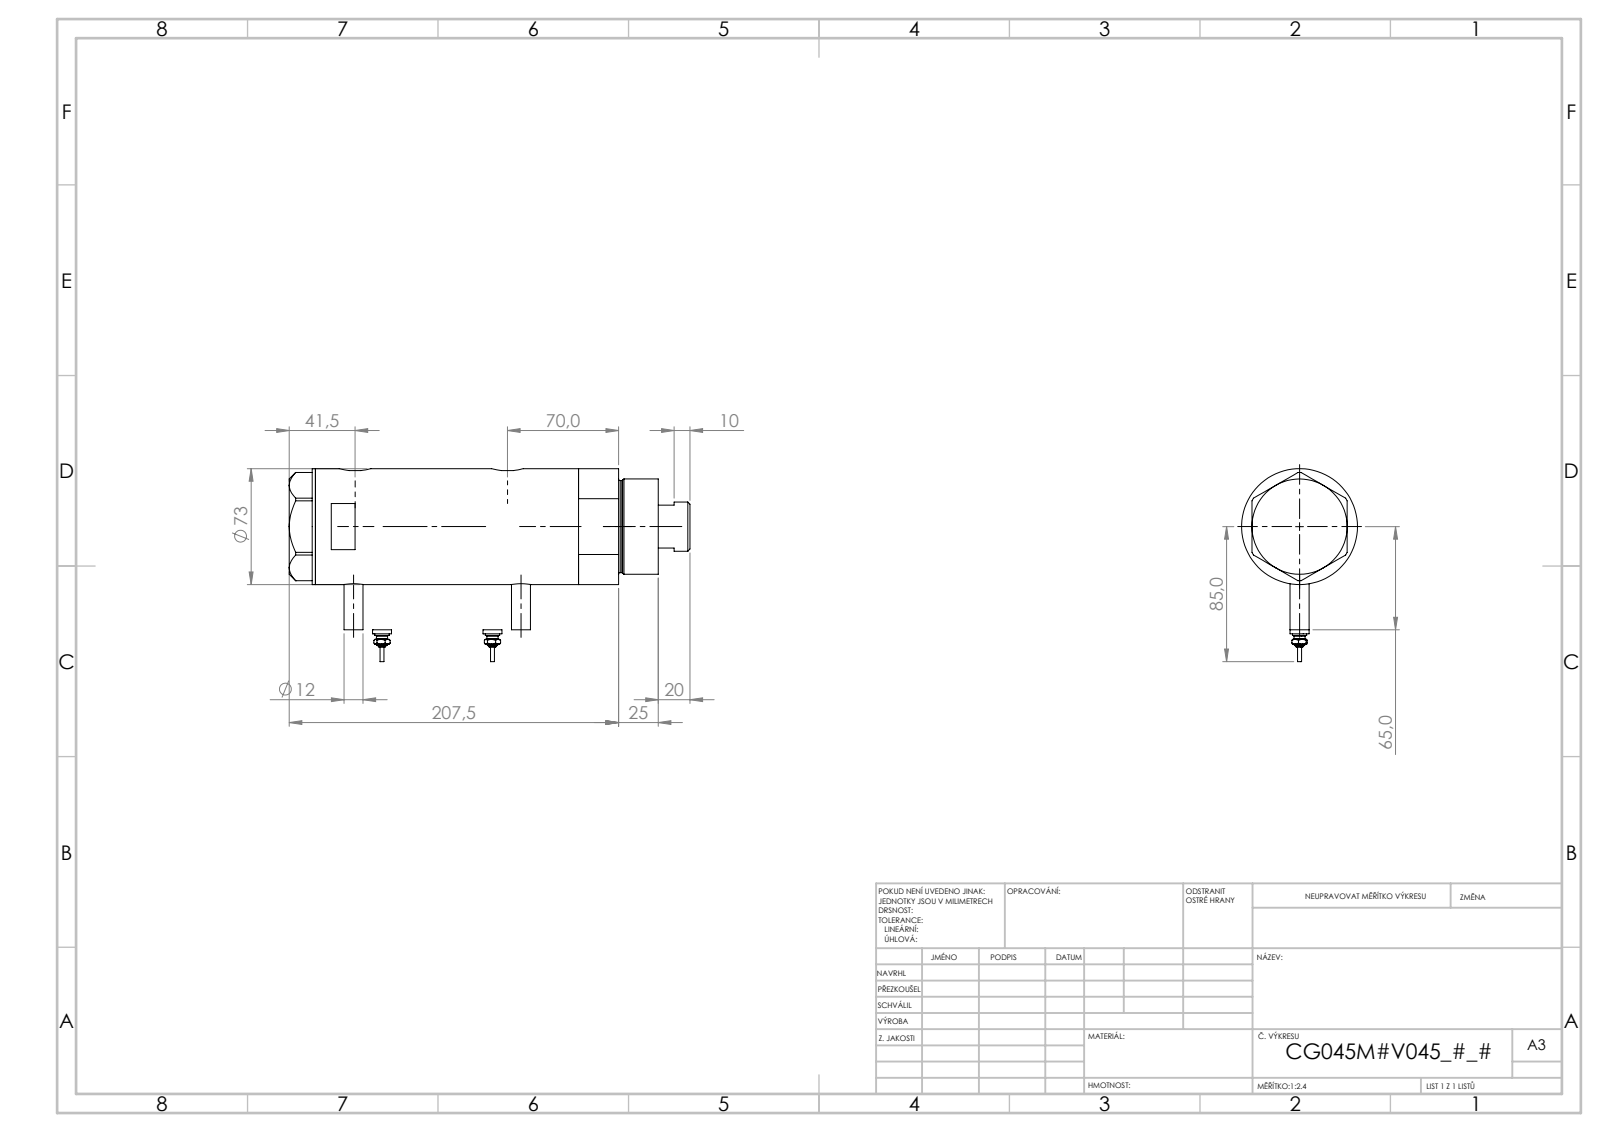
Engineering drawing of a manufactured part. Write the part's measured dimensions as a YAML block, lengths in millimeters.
part_name: "V270CG_FRONT; V270CG_BACK; V270CG_SWITCH; V270CG_VC (+1 more)"
step_written_by: "SolidWorks 2019 (CONFIG_CONTROL_DESIGN)"
units: millimeters
bodies: {solids: 6, faces: 231, planar: 78, cylindrical: 79, other: 74}
overall_size: [236.52, 105.3, 73]
volume: 822576
surface_area: 143093
round_holes:
  - {diameter: 5, count: 2}
  - {diameter: 12.5, count: 2}
  - {diameter: 13.16, count: 2}
  - {diameter: 10.5, count: 1}
  - {diameter: 32, count: 1}
  - {diameter: 33.5, count: 1}
  - {diameter: 45, count: 1}
  - {diameter: 48, count: 1}
  - {diameter: 64, count: 1}
round_bosses_or_shafts:
  - {diameter: 12, count: 3}
  - {diameter: 9, count: 2}
  - {diameter: 7, count: 2}
  - {diameter: 4.34, count: 2}
  - {diameter: 2.4, count: 2}
  - {diameter: 73, count: 1}
  - {diameter: 60, count: 1}
  - {diameter: 58, count: 1}
partial_cylinders:
  - {radius: 10, count: 2}
face_to_face_distances: [112.14, 26, 86.14, 16.5, 42.5, 128.64, 200.01, 216.51, 174.01, 87.87]
hole_center_spacings: [96.65, 0.99, 1, 8.5, 8.51, 87.15, 88.14, 88.15]
